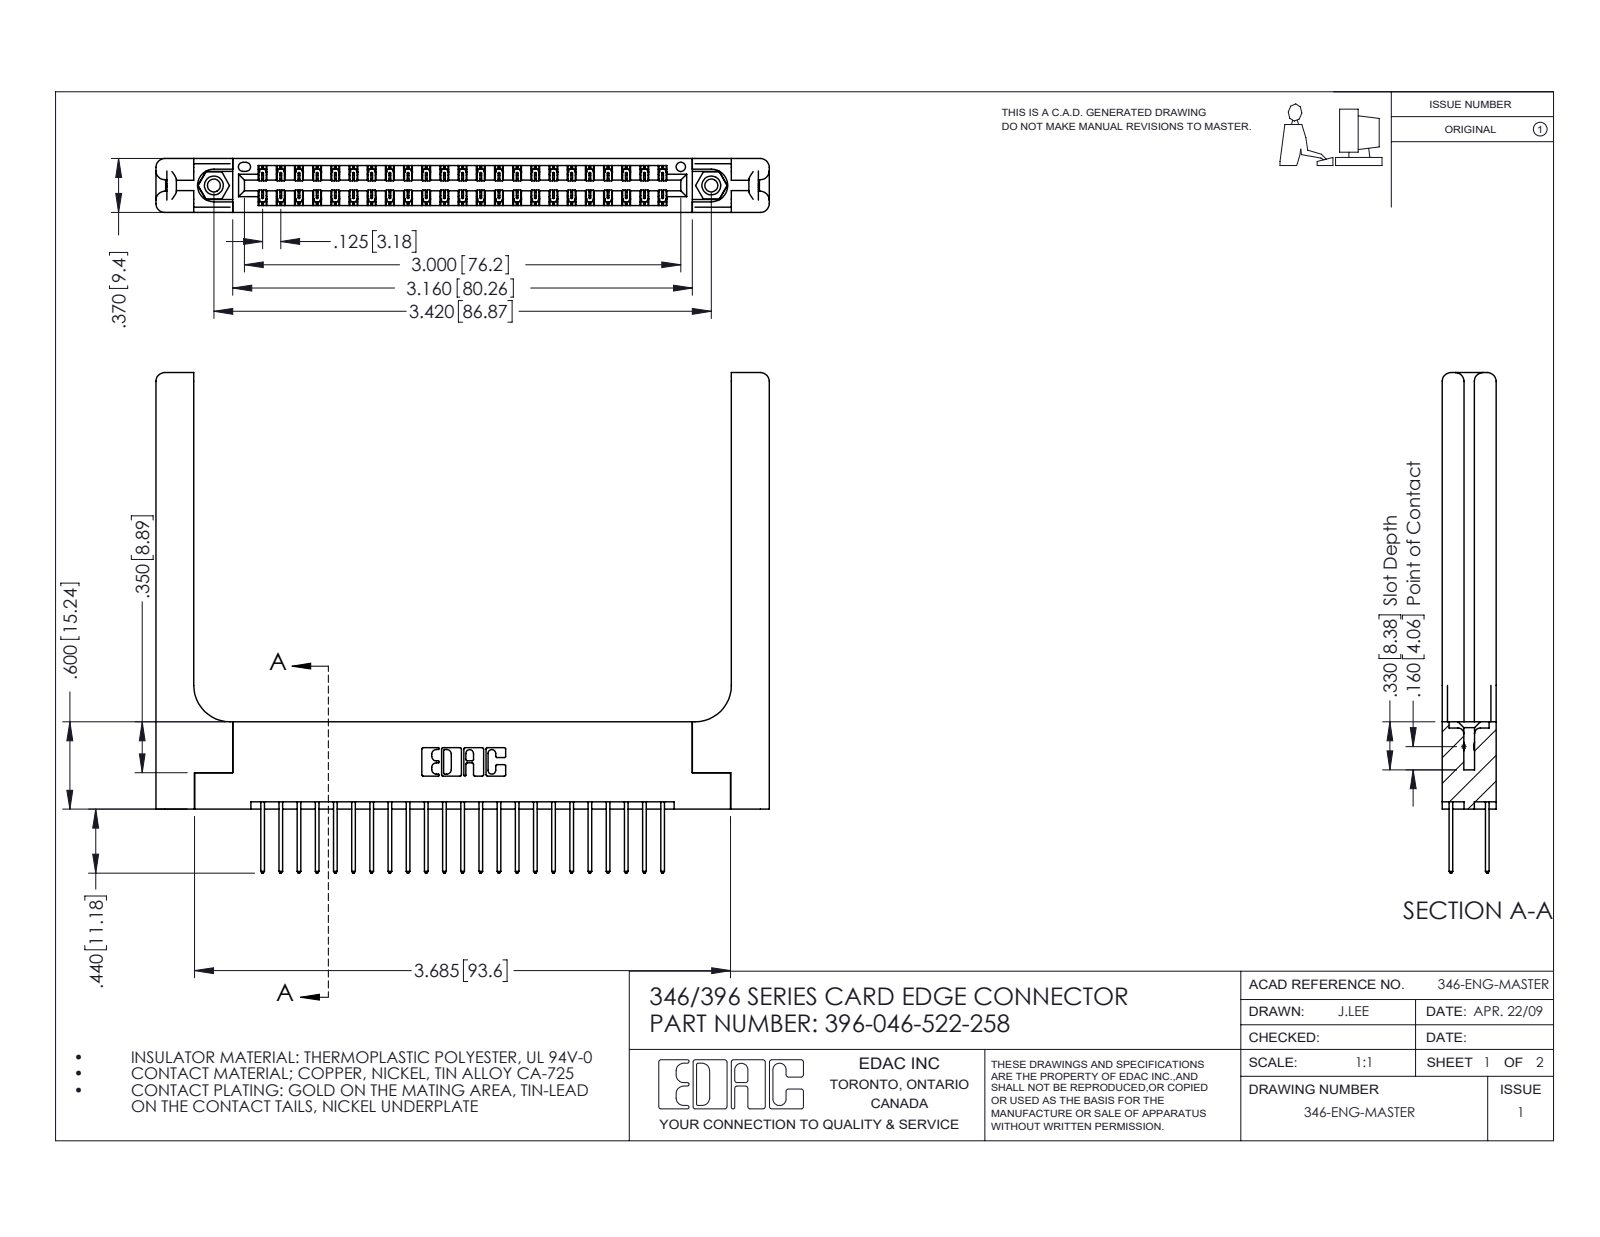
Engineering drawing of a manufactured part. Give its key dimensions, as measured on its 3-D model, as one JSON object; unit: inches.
{"part_name": "346 Part_Flush Mounting Lugs - 0.156 Dia-TH; 345-250-001_345-250-001-102; 346-220-058_345-220-058; 396-046-522-258 (+1 more)", "step_written_by": "SolidWorks 2016 (CONFIG_CONTROL_DESIGN)", "units": "inches", "bodies": {"solids": 51, "faces": 2770, "planar": 1834, "cylindrical": 876, "other": 60}, "overall_size": [4.216, 3.44, 0.37], "volume_in3": 1.093, "surface_area_in2": 30.28, "round_holes": [[0.089, 2], [0.125, 2], [0.156, 2], [0.064, 1]], "round_bosses_or_shafts": [[0.155, 2]], "partial_cylinders_radius": [[0.006, 69], [0.01, 46], [0.01, 22], [0.06, 16], [0.007, 6], [0.031, 6], [0.026, 3], [0.014, 2]], "face_to_face_distances": [0.37, 0.072, 0.048, 0.322, 0.25, 0.148, 0.15, 0.025, 0.298, 0.275], "hole_center_spacings": [0.246, 3.212, 3.42]}
